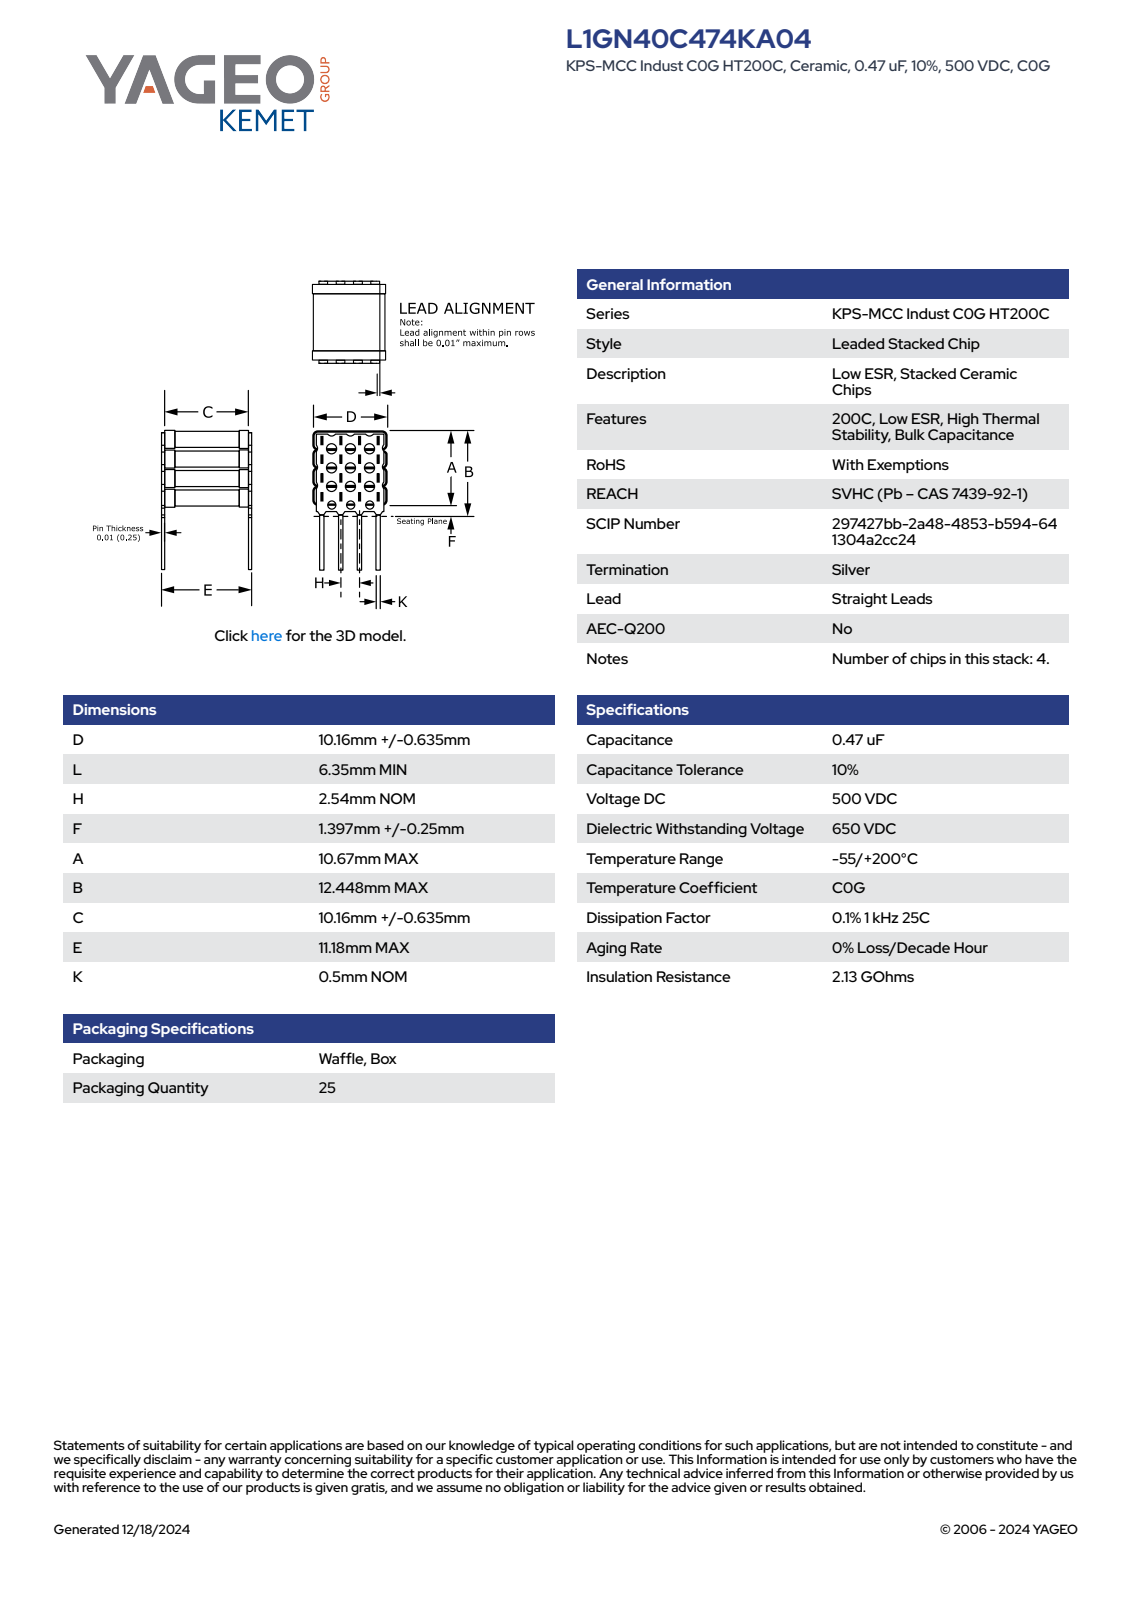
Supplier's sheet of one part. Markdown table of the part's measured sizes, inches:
| quantity | value |
| --- | --- |
| part name | CCSS_LSN4_4_D10.795L6.35H2.54F1.647A10.67B12.448C10.795E11.18K0.5 |
| STEP written by | SolidWorks 2014 (AUTOMOTIVE_DESIGN) |
| units | inches |
| bodies | 4 solids, 199 faces (199 planar, 0 cylindrical, 0 other) |
| overall size | 0.74 × 0.443 × 0.425 |
| volume | 0.075 in³ |
| surface area | 2.446 in² |
| main face-to-face distances | 0.106, 0.212, 0.105, 0.211, 0.317, 0.097, 0.203, 0.309, 0.114, 0.098 |
